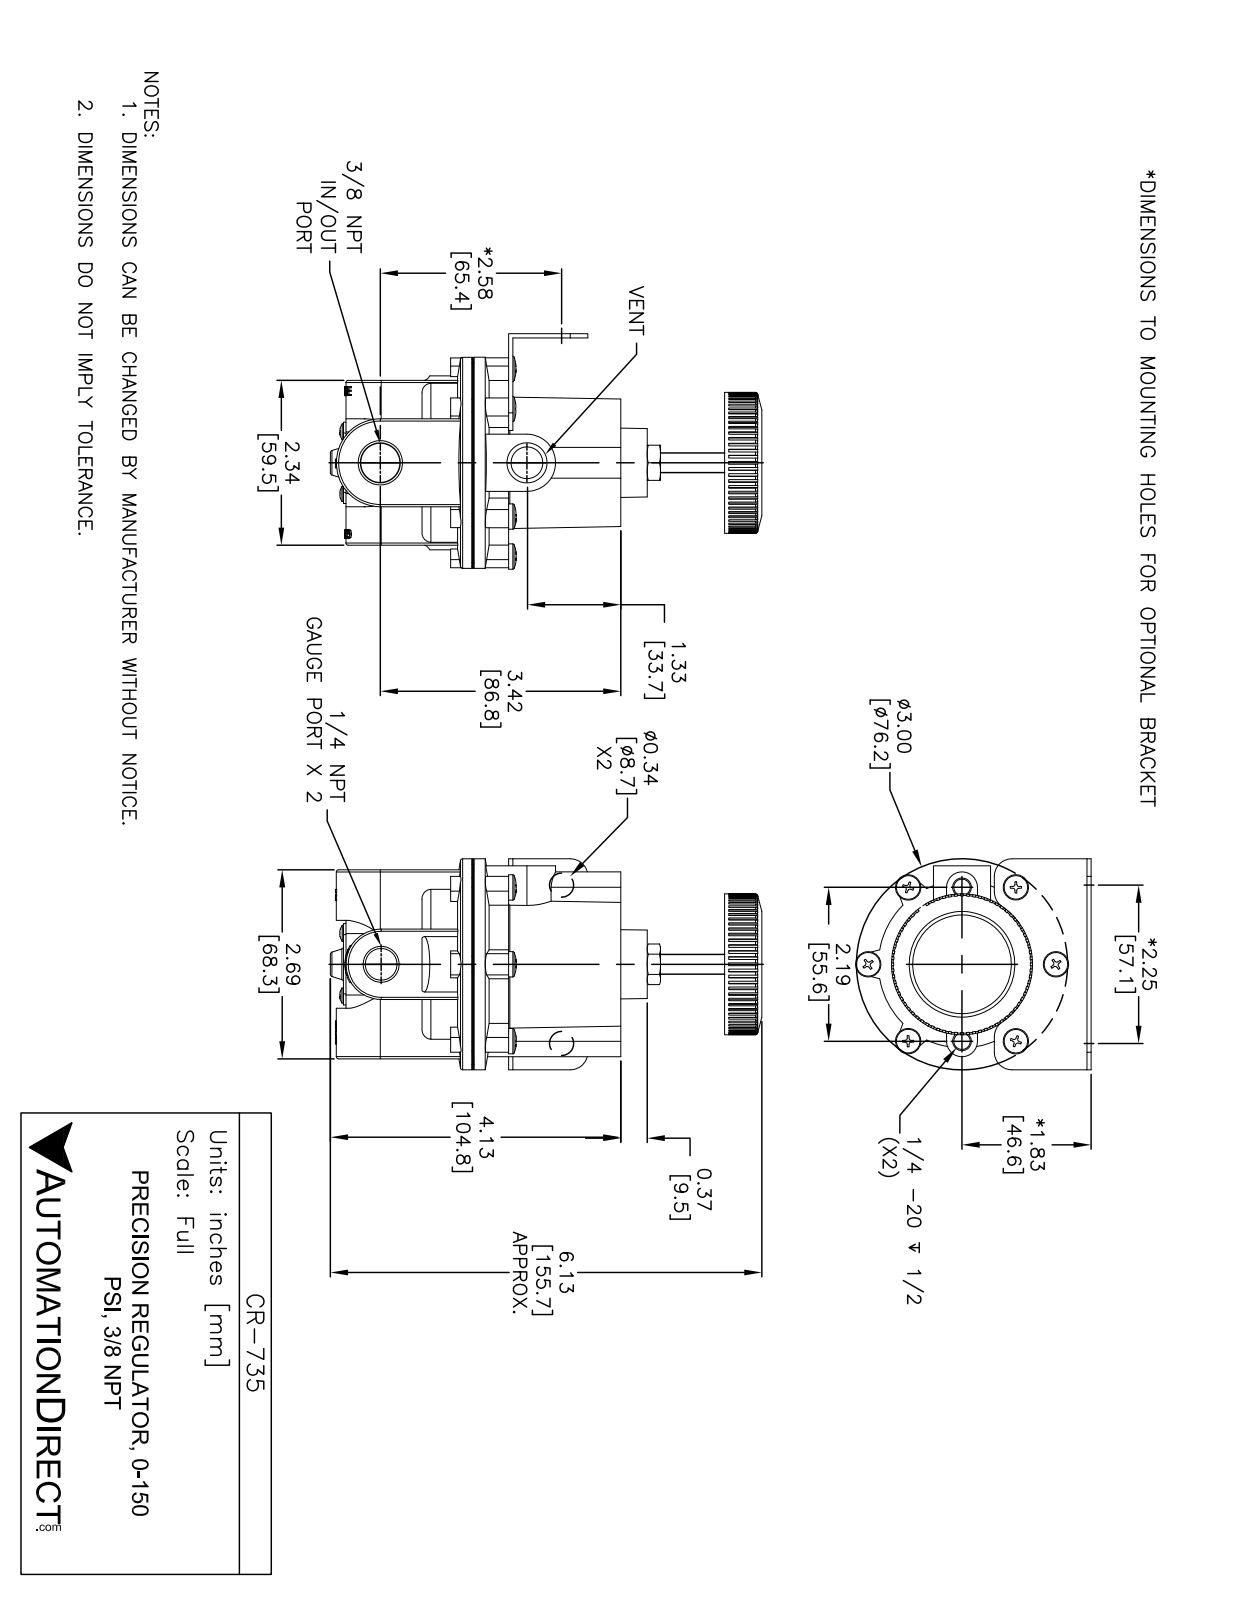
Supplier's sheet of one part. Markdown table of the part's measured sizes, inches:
| quantity | value |
| --- | --- |
| part name | CR-735 |
| STEP written by | SolidWorks 2015 (CONFIG_CONTROL_DESIGN) |
| units | inches |
| bodies | 10 solids, 1525 faces (521 planar, 817 cylindrical, 187 other) |
| overall size | 6.123 × 3.041 × 3 |
| volume | 17.33 in³ |
| surface area | 88.44 in² |
| round holes (diameter × count) | 0.201 × 8, 0.159 × 6, 0.438 × 2, 0.562 × 1, 1.403 × 1, 1.683 × 1 |
| round bosses / shafts (diameter × count) | 0.373 × 6, 0.19 × 6, 0.149 × 6, 3 × 1, 2 × 1, 0.628 × 1, 0.281 × 1 |
| partial cylindrical surfaces (radius × count) | 0.004 × 72, 0.02 × 18, 0.032 × 6, 0.156 × 6, 0.157 × 6, 0.141 × 4, 0.187 × 3, 0.033 × 2 |
| main face-to-face distances | 0.034, 2.114, 2.08, 0.524, 0.49, 1.59, 3.879, 3.845, 3.355, 1.765 |
| hole center spacings | 1.334, 1.725, 2.317, 0.765, 0.765, 1.094, 1.232, 1.232 |
